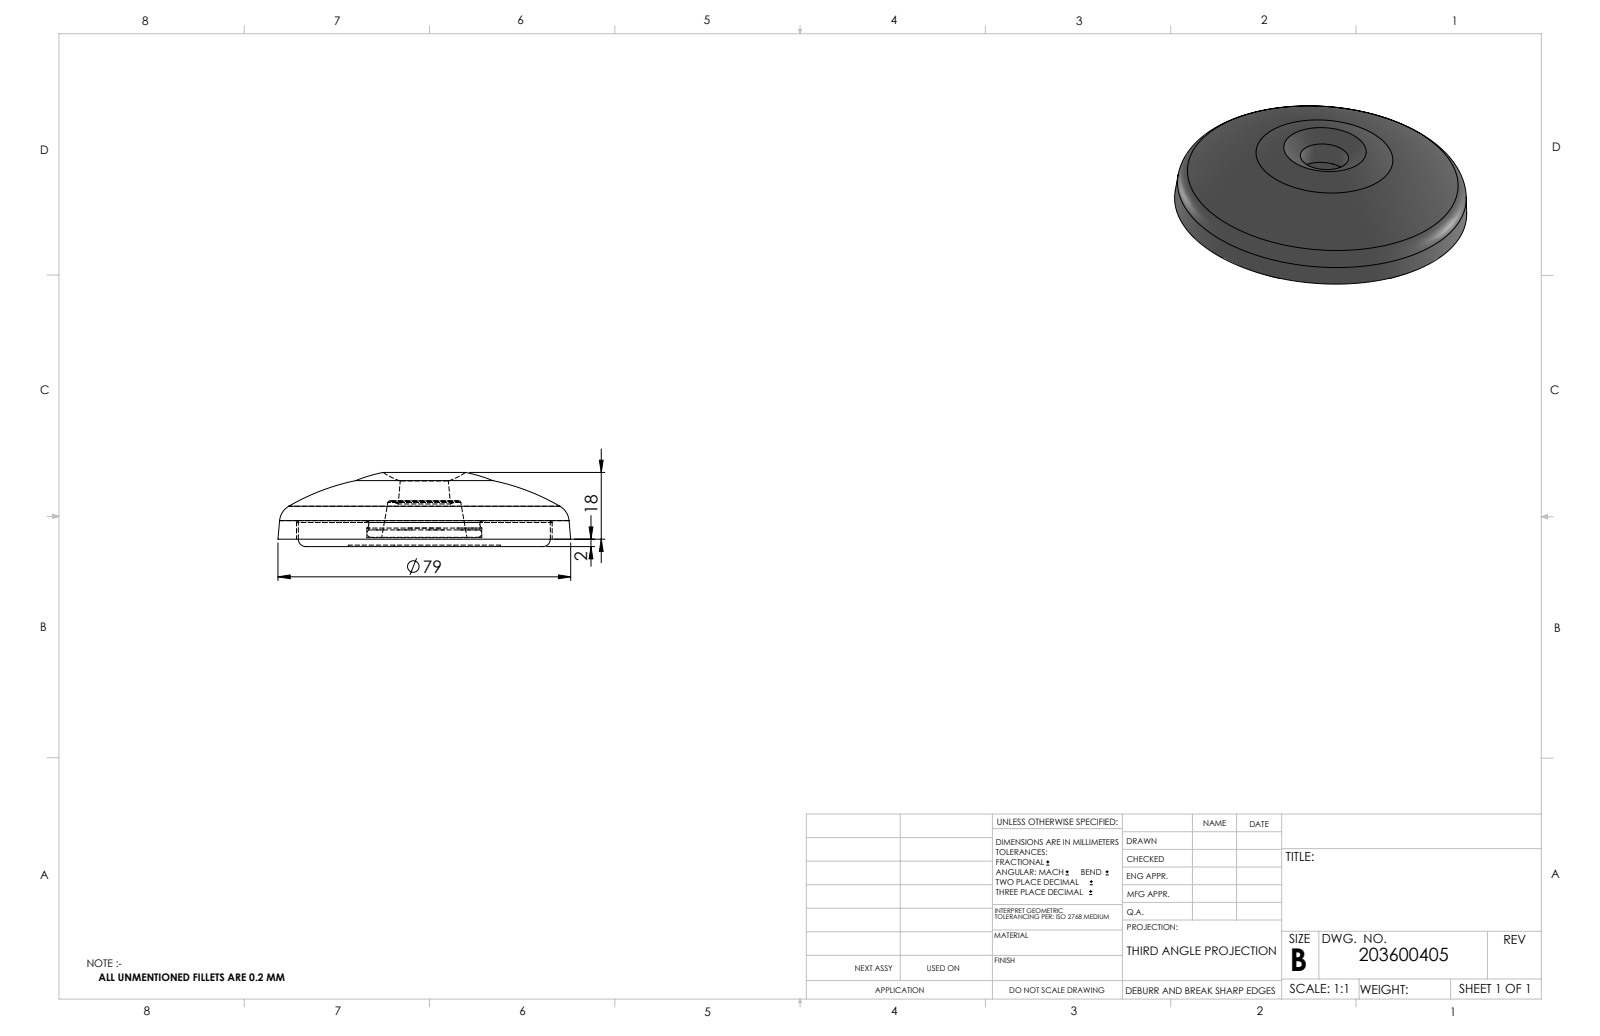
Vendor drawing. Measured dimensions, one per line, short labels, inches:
name: 203600405_c_1
written by: SolidWorks 2014 (CONFIG_CONTROL_DESIGN)
unit: in
bodies: 1 solid, 47 faces (7 planar, 12 cylindrical, 28 other)
size: 3.11 × 3.11 × 0.787
volume: 3.889 in³; area: 26.78 in²
holes: 1× ⌀1.22, 1× ⌀1.614, 1× ⌀2.717
bosses: 1× ⌀2.677, 1× ⌀1.181, 1× ⌀0.63
face distances: 0.079, 0.016, 0.063, 0.094, 0.098, 0.083, 0.02, 0.276, 0.26, 0.197
